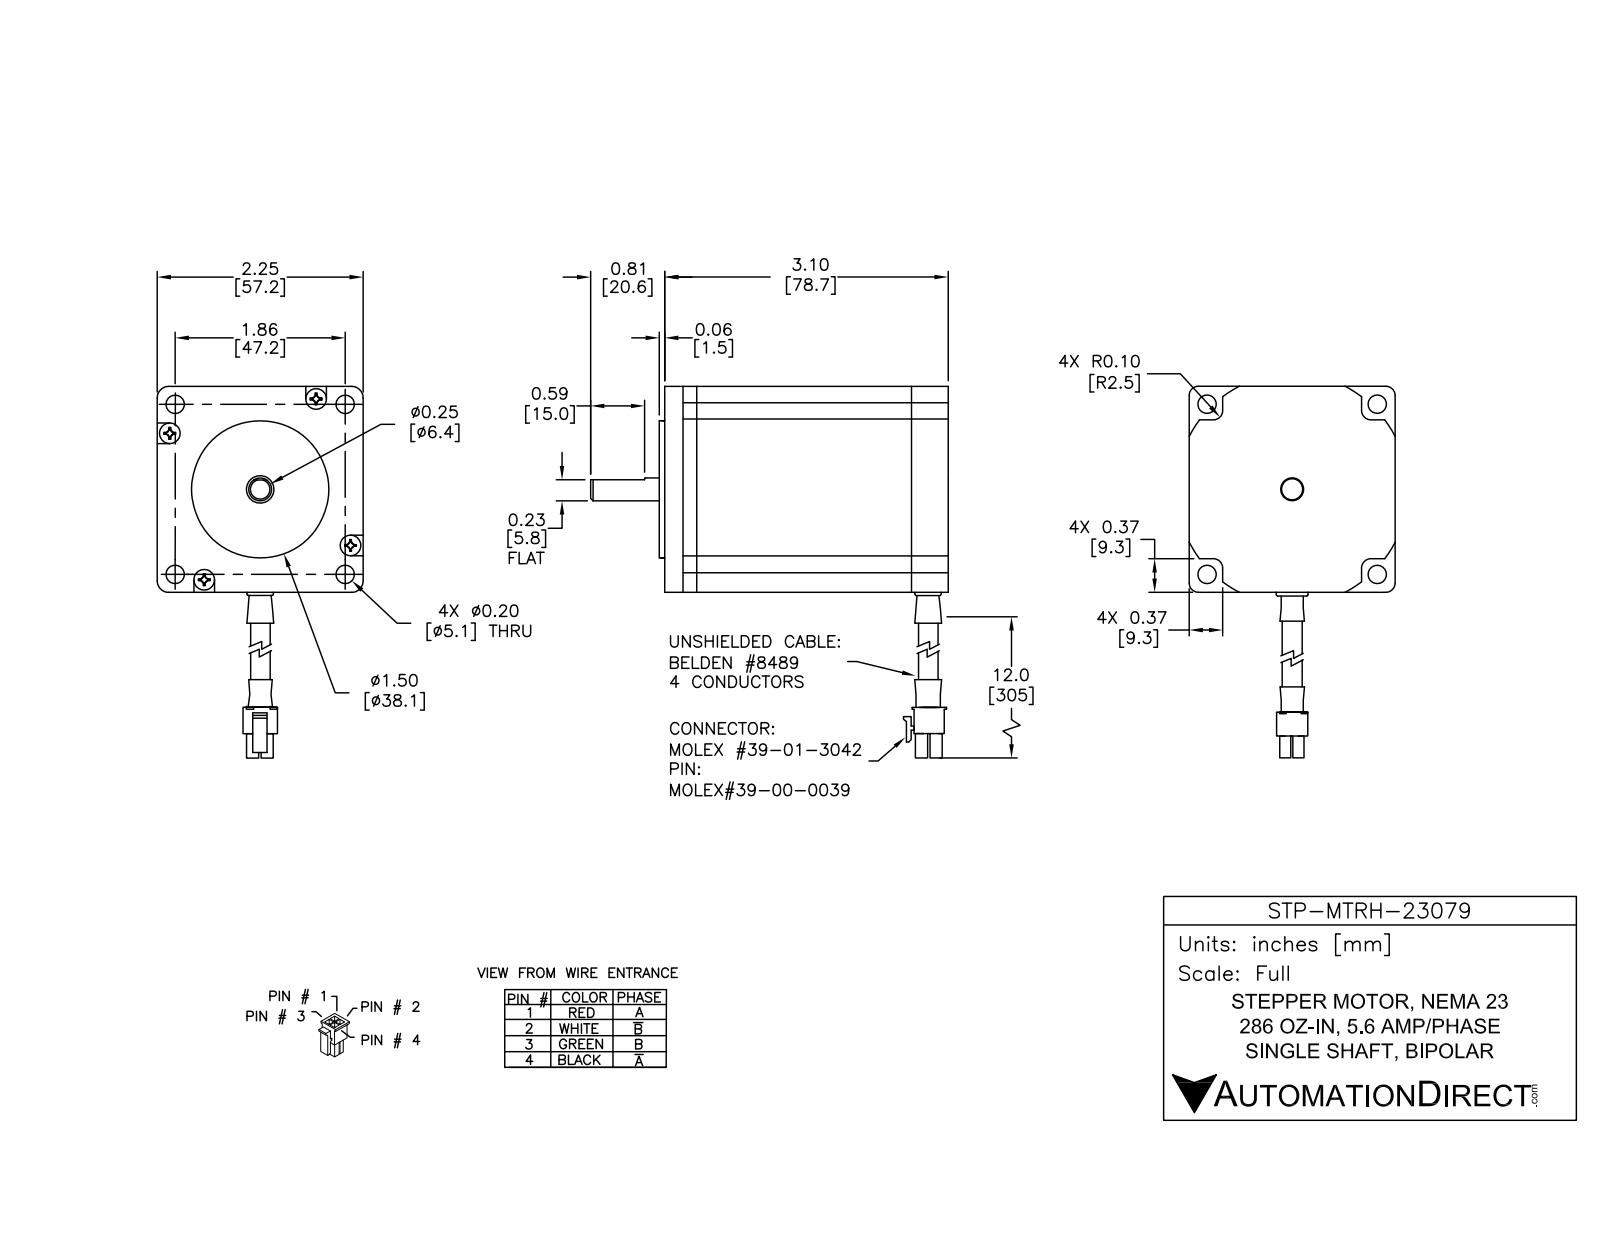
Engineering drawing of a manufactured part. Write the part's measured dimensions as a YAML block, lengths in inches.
part_name: "STP-MTRH-23079"
step_written_by: "SolidWorks 2014 (AUTOMOTIVE_DESIGN)"
units: inches
bodies: {solids: 17, faces: 1915, planar: 838, cylindrical: 956, other: 121}
overall_size: [14.207, 3.783, 2.207]
volume: 9.541
surface_area: 140.6
round_holes:
  - {diameter: 0.2, count: 5}
  - {diameter: 0.097, count: 4}
  - {diameter: 0.118, count: 4}
  - {diameter: 0.063, count: 1}
  - {diameter: 0.295, count: 1}
  - {diameter: 0.394, count: 1}
  - {diameter: 0.398, count: 1}
  - {diameter: 0.45, count: 1}
  - {diameter: 0.474, count: 1}
  - {diameter: 0.65, count: 1}
  - {diameter: 0.7, count: 1}
  - {diameter: 0.707, count: 1}
round_bosses_or_shafts:
  - {diameter: 0.125, count: 8}
  - {diameter: 0.205, count: 4}
  - {diameter: 0.126, count: 4}
  - {diameter: 0.05, count: 4}
  - {diameter: 1.5, count: 1}
  - {diameter: 1.44, count: 1}
  - {diameter: 1.375, count: 1}
  - {diameter: 1.372, count: 1}
partial_cylinders:
  - {radius: 0.025, count: 100}
  - {radius: 0.03, count: 46}
  - {radius: 0.02, count: 40}
  - {radius: 0.012, count: 8}
  - {radius: 0.14, count: 8}
  - {radius: 0.039, count: 4}
  - {radius: 0.125, count: 4}
  - {radius: 0.129, count: 4}
face_to_face_distances: [2.207, 0.865, 1.065, 0.139, 2.069, 1.93, 0.048, 0.913, 1.113, 1.978]
hole_center_spacings: [0.315, 0.316, 1.159, 1.16, 1.236, 1.314, 1.548, 1.548]
